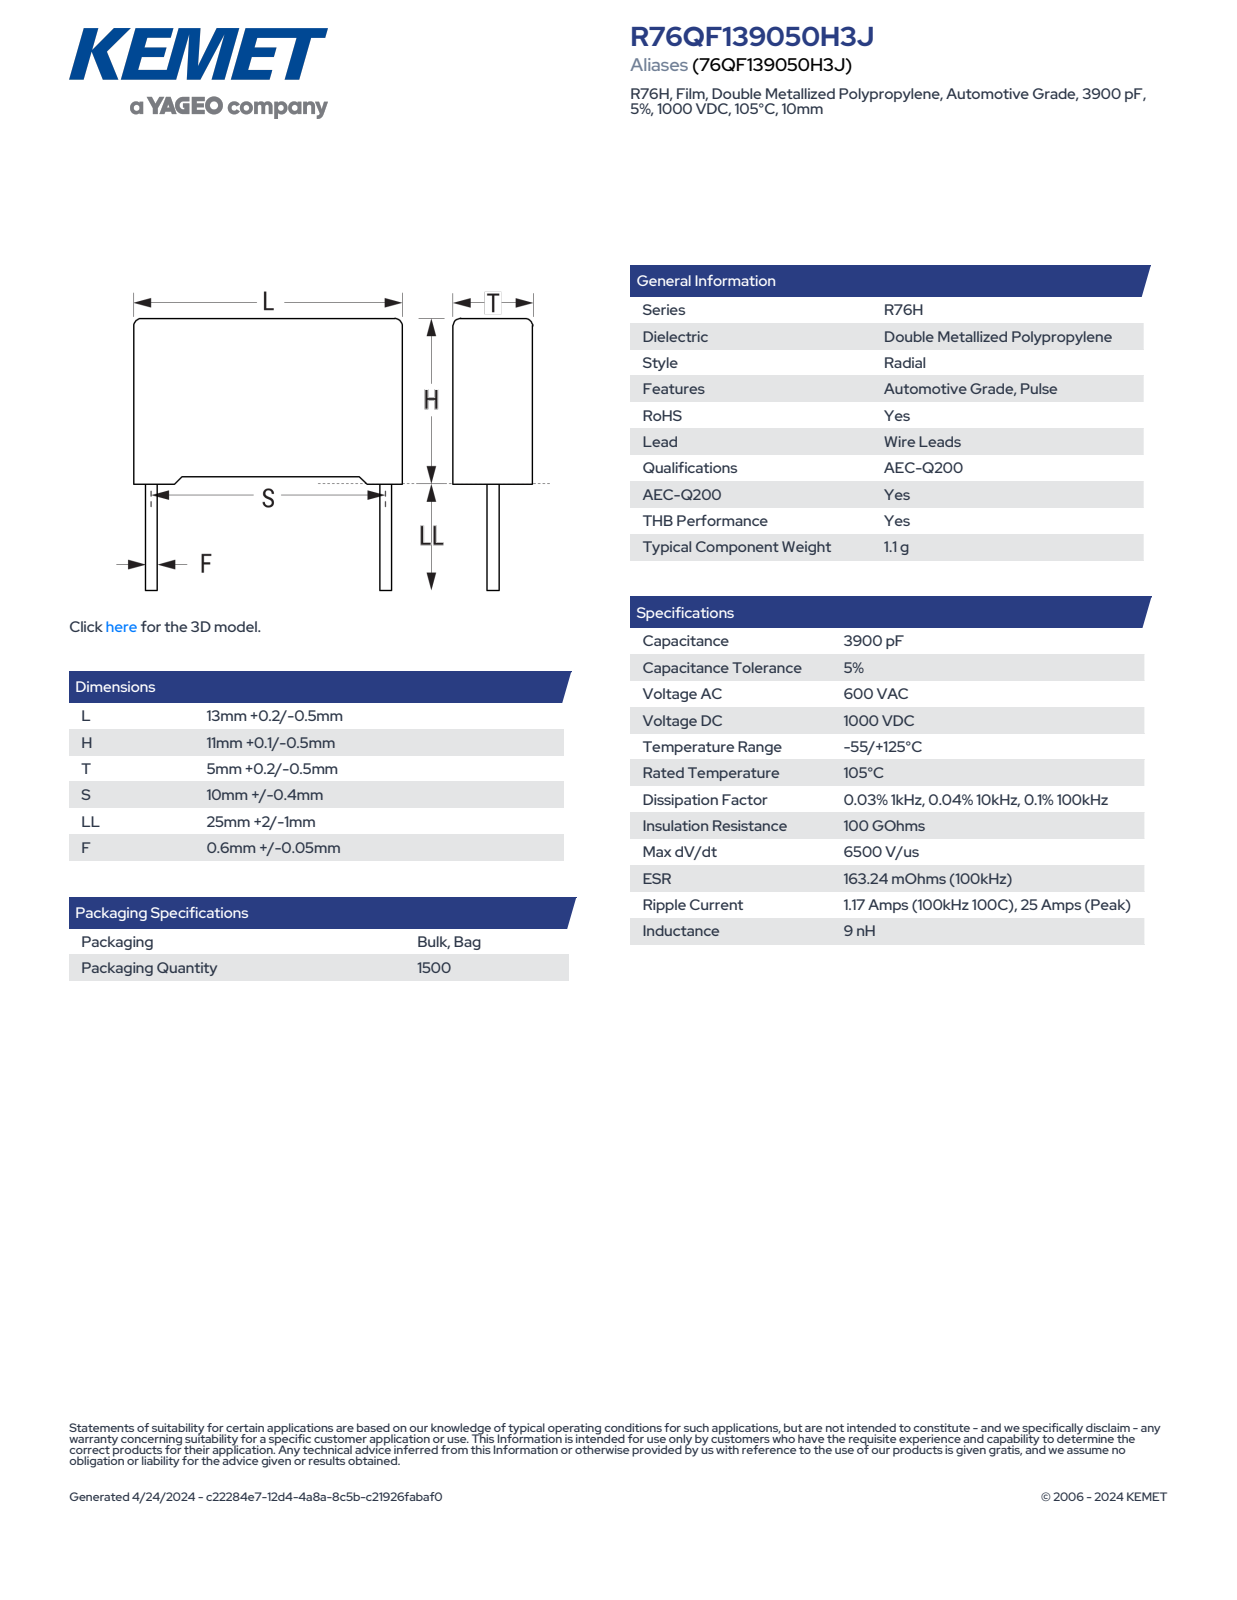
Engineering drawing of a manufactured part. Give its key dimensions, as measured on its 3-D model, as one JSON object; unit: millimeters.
{"part_name": "CFR_RB2R76_13X11X5_L13.2H11.1T5.2S10LL27F0.65", "step_written_by": "SolidWorks 2014 (AUTOMOTIVE_DESIGN)", "units": "millimeters", "bodies": {"solids": 4, "faces": 85, "planar": 77, "cylindrical": 8, "other": 0}, "overall_size": [38.1, 13.2, 5.21], "volume_mm3": 736, "surface_area_mm2": 679, "round_bosses_or_shafts": [[0.65, 2]], "partial_cylinders_radius": [[0.5, 4]], "face_to_face_distances": [5.2, 13.2, 10.35, 0.44, 4.76, 0.75, 11.1, 4.32, 12.76, 0.37]}
